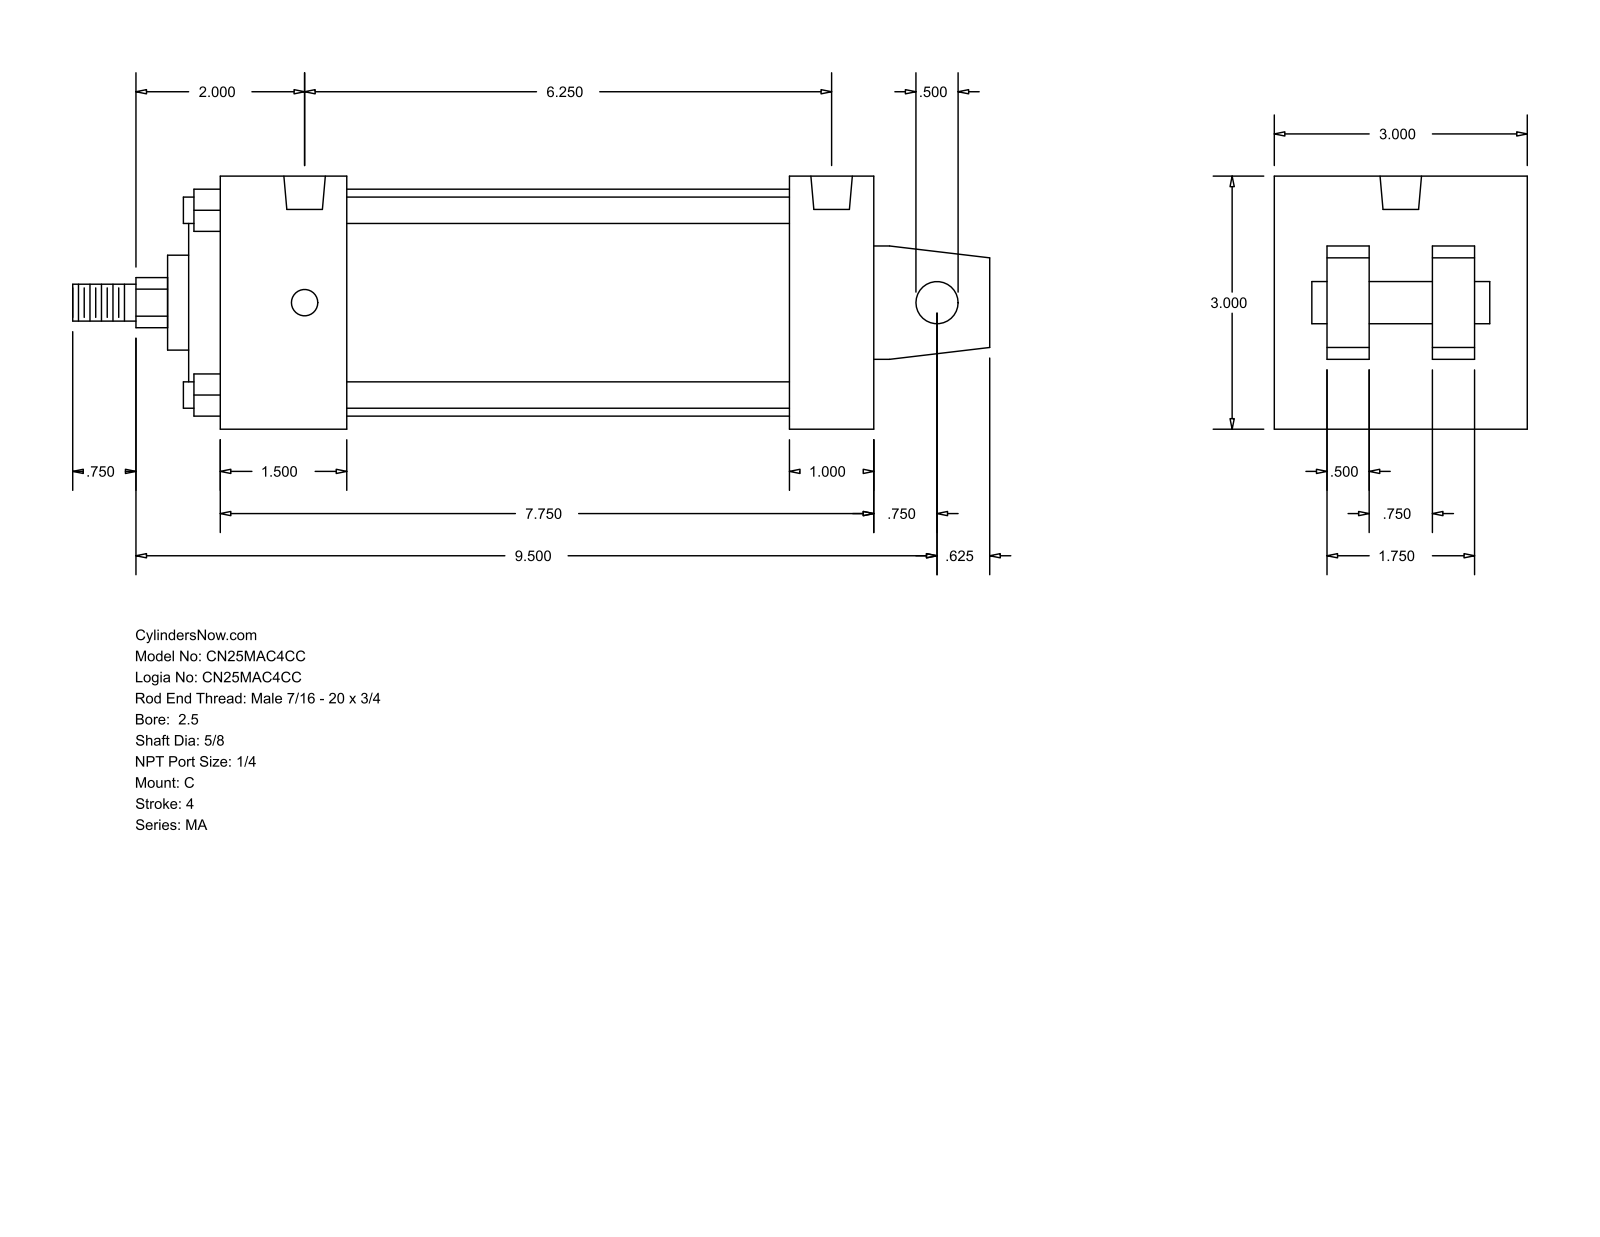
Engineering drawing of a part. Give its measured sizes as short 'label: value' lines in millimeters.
name: MA_C__0250_0.625
written by: GSSL Pune (CONFIG_CONTROL_DESIGN)
unit: mm
bodies: 0 solids, 105 faces (77 planar, 28 cylindrical, 0 other)
size: 276.23 × 76.2 × 76.2
holes: 4× ⌀7.94, 2× ⌀12.49
bosses: 4× ⌀7.94, 1× ⌀68.33, 1× ⌀50.8, 1× ⌀28.57, 1× ⌀15.88, 1× ⌀12.7, 1× ⌀11.11
rounds: 1× R7.54
face distances: 76.2, 196.85, 12.7, 15.87, 60.33, 47.63, 25.4, 38.1, 171.45, 133.35
hole spacings: 158.75
